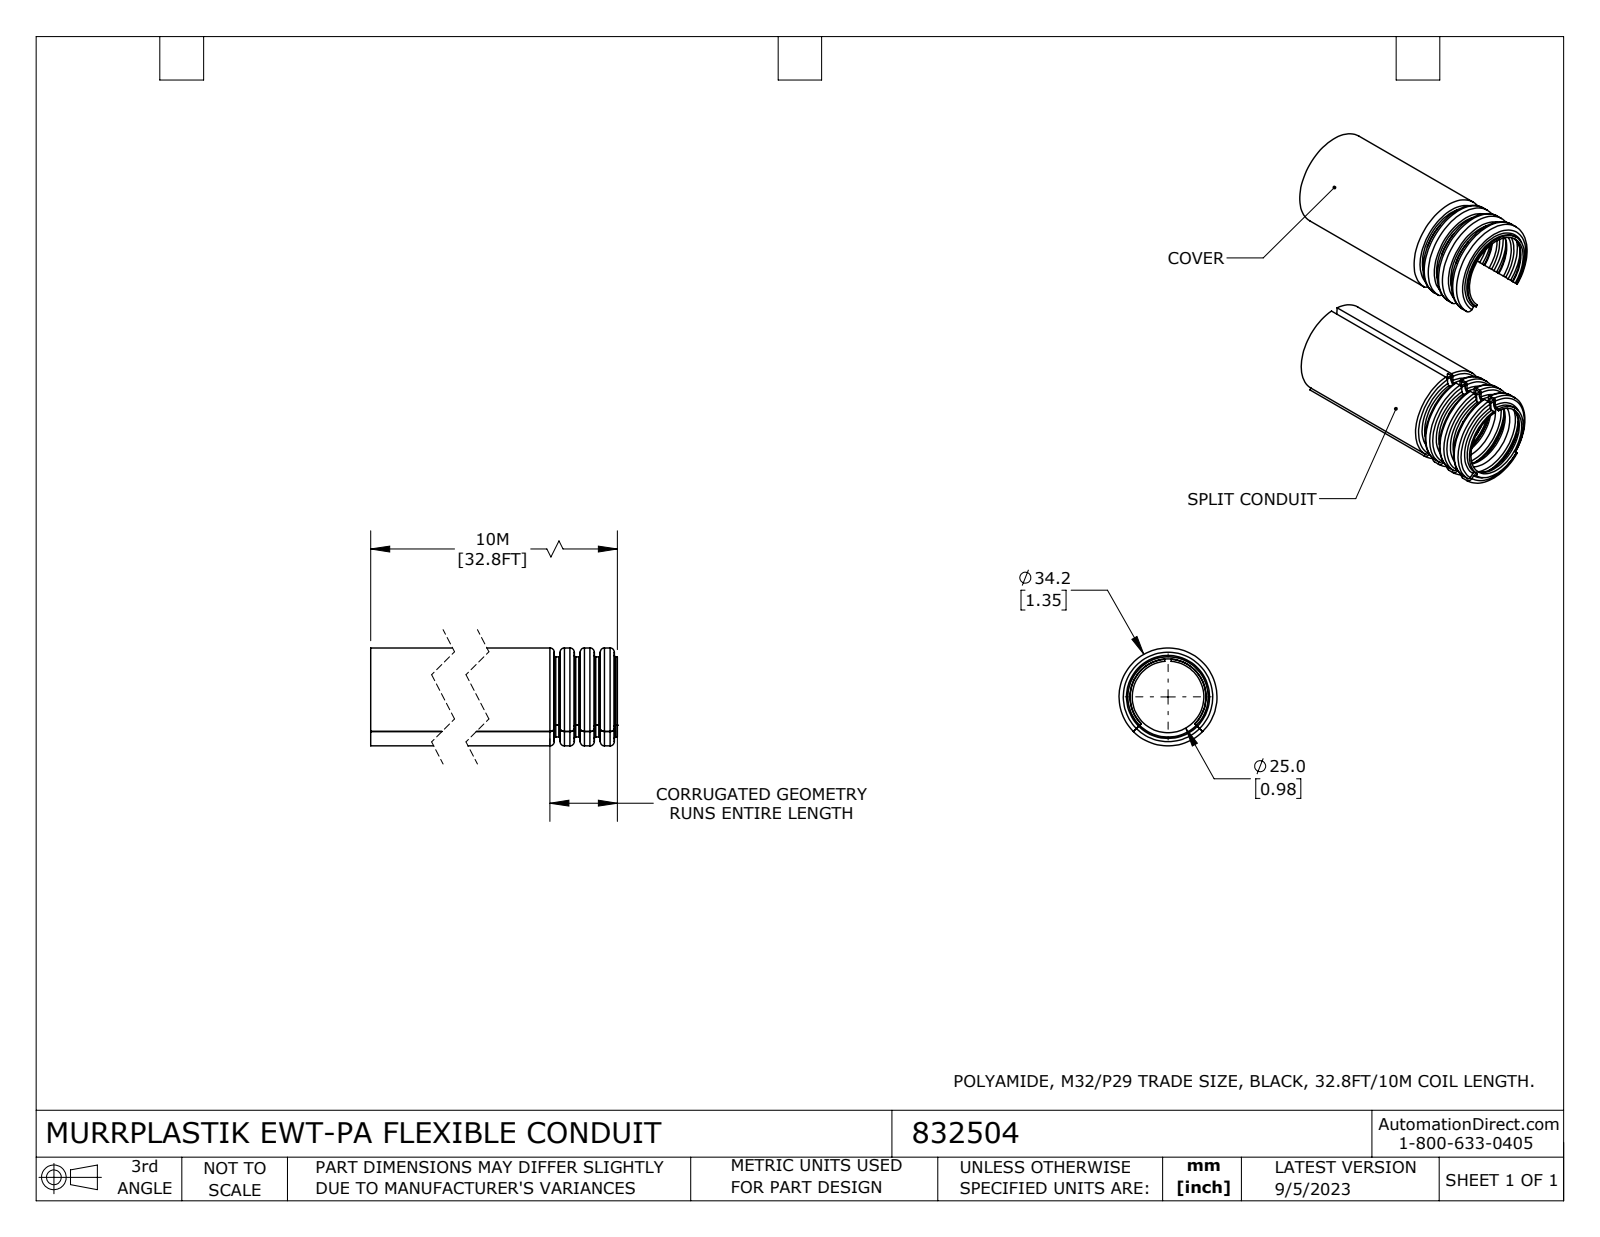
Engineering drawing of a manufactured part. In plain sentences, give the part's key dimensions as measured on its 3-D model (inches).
The part is named "832504". Its 3-D file was written by "SolidWorks 2021 (CONFIG_CONTROL_DESIGN)". It is 2 solids with 341 faces: 10 planar, 107 cylindrical and 224 other. Overall it measures 3.15 by 1.346 by 1.346 inches. Its volume is 1.752 cubic inches and its surface area 51.6 square inches. Round holes: 1 of diameter 0.984, 1 of diameter 1.228. Round bosses or shafts: 1 of diameter 1.346, 1 of diameter 1.102. Partial cylindrical surfaces (rounded edges, fillets, slot ends): 1 of radius 0.522, 1 of radius 0.644. The main face-to-face distances are 3.15.
